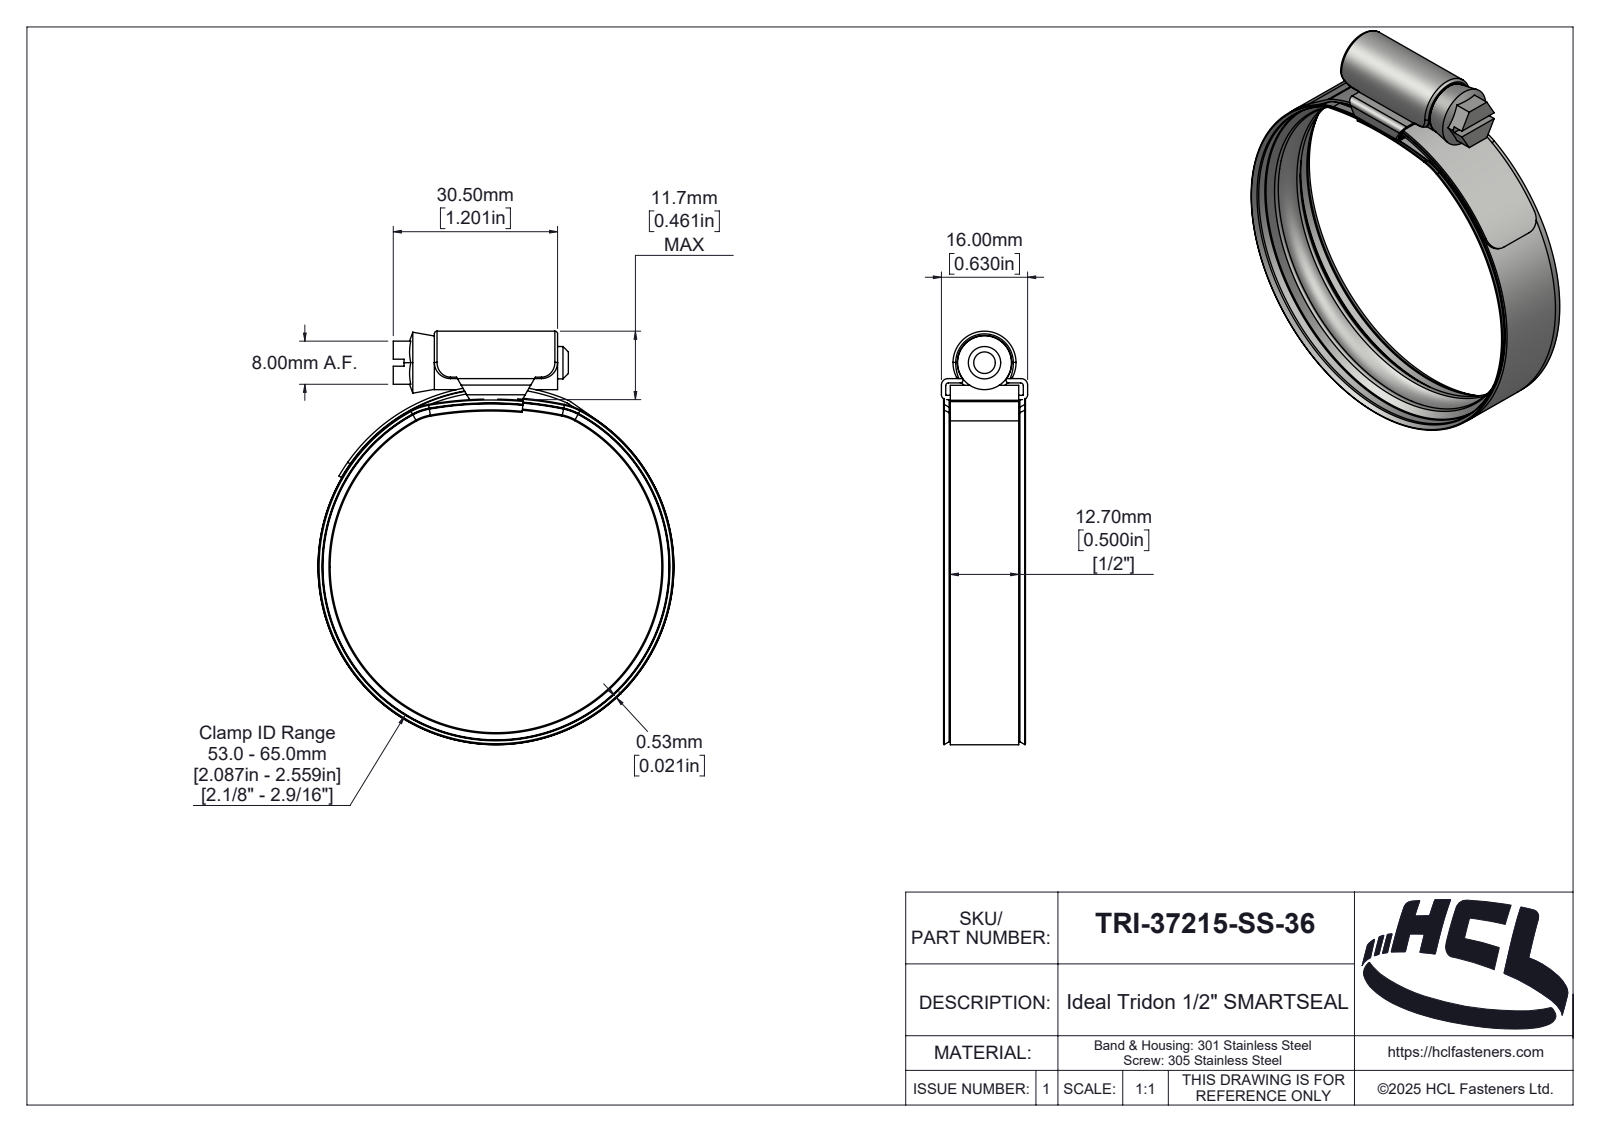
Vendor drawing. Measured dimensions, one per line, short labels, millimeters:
name: TRI-37215-SS-36
written by: SolidWorks 2025 (AUTOMOTIVE_DESIGN)
unit: mm
bodies: 4 solids, 418 faces (42 planar, 119 cylindrical, 257 other)
size: 76.73 × 66.06 × 16
volume: 5 387 mm³; area: 16 525 mm²
holes: 1× ⌀64.4, 1× ⌀65
bosses: 1× ⌀66.06, 1× ⌀64.8, 1× ⌀10, 1× ⌀6
rounds: 6× R0.5, 4× R3, 2× R0.1, 2× R0.9, 2× R1.2, 2× R9.9, 2× R10.1, 1× R0.46
face distances: 0.8, 3.1, 12.7, 0.53, 2.3, 30.5, 3.9, 1.65, 14.35, 15.2
